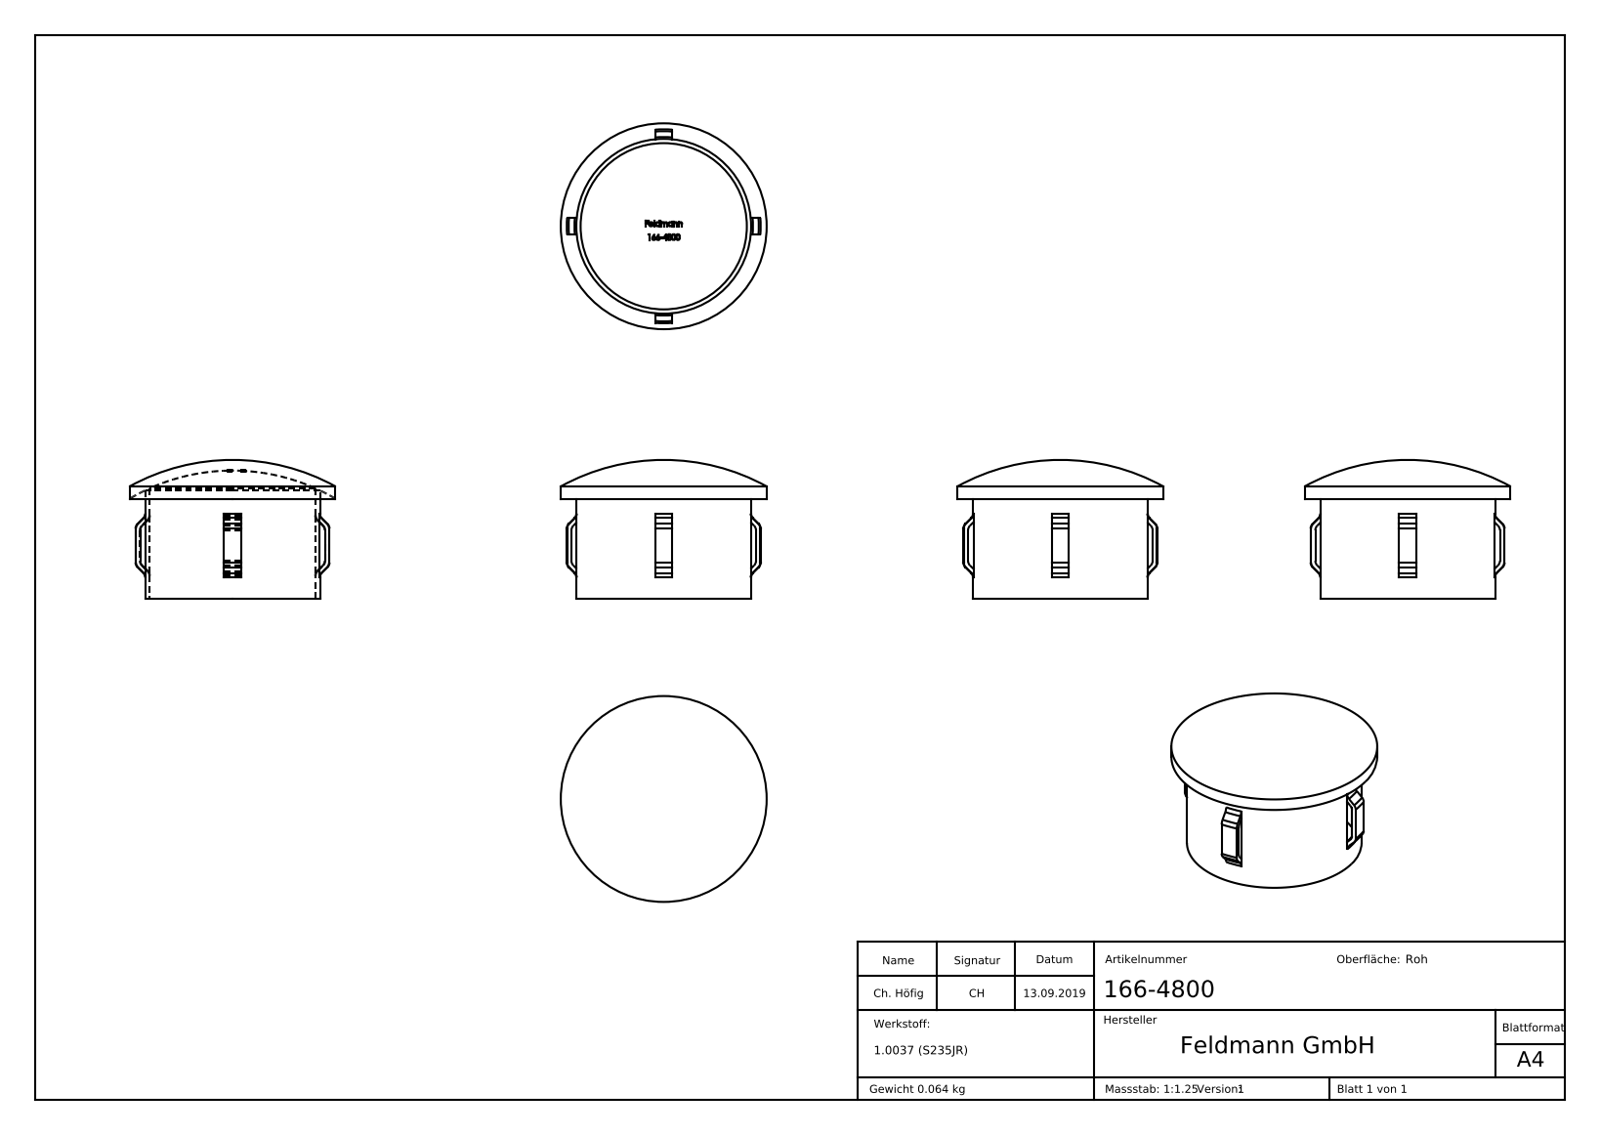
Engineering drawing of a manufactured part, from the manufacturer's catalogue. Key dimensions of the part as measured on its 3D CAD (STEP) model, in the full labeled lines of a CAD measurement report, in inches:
Part name (STEP PRODUCT): 166-4800
STEP written by: SolidWorks 2015 (CONFIG_CONTROL_DESIGN)
Units: inches
Bodies: 1 solid, 318 faces (100 planar, 16 cylindrical, 202 other)
Overall size (bounding box): 1.902 × 1.902 × 1.283
Volume: 0.498 in³ · Surface area: 17.16 in²
Round holes (diameter × count): ⌀1.535 ×1
Round bosses / shafts (diameter × count): ⌀1.902 ×1, ⌀1.614 ×1
Partial cylindrical surfaces — rounded edges, fillets, slot ends (radius × count): R0.856 ×1, R0.896 ×1
Main face-to-face distances: 0.157, 0.079, 0.117, 0.112, 0.015, 0.05, 0.056, 0.153, 0.129, 0.132
